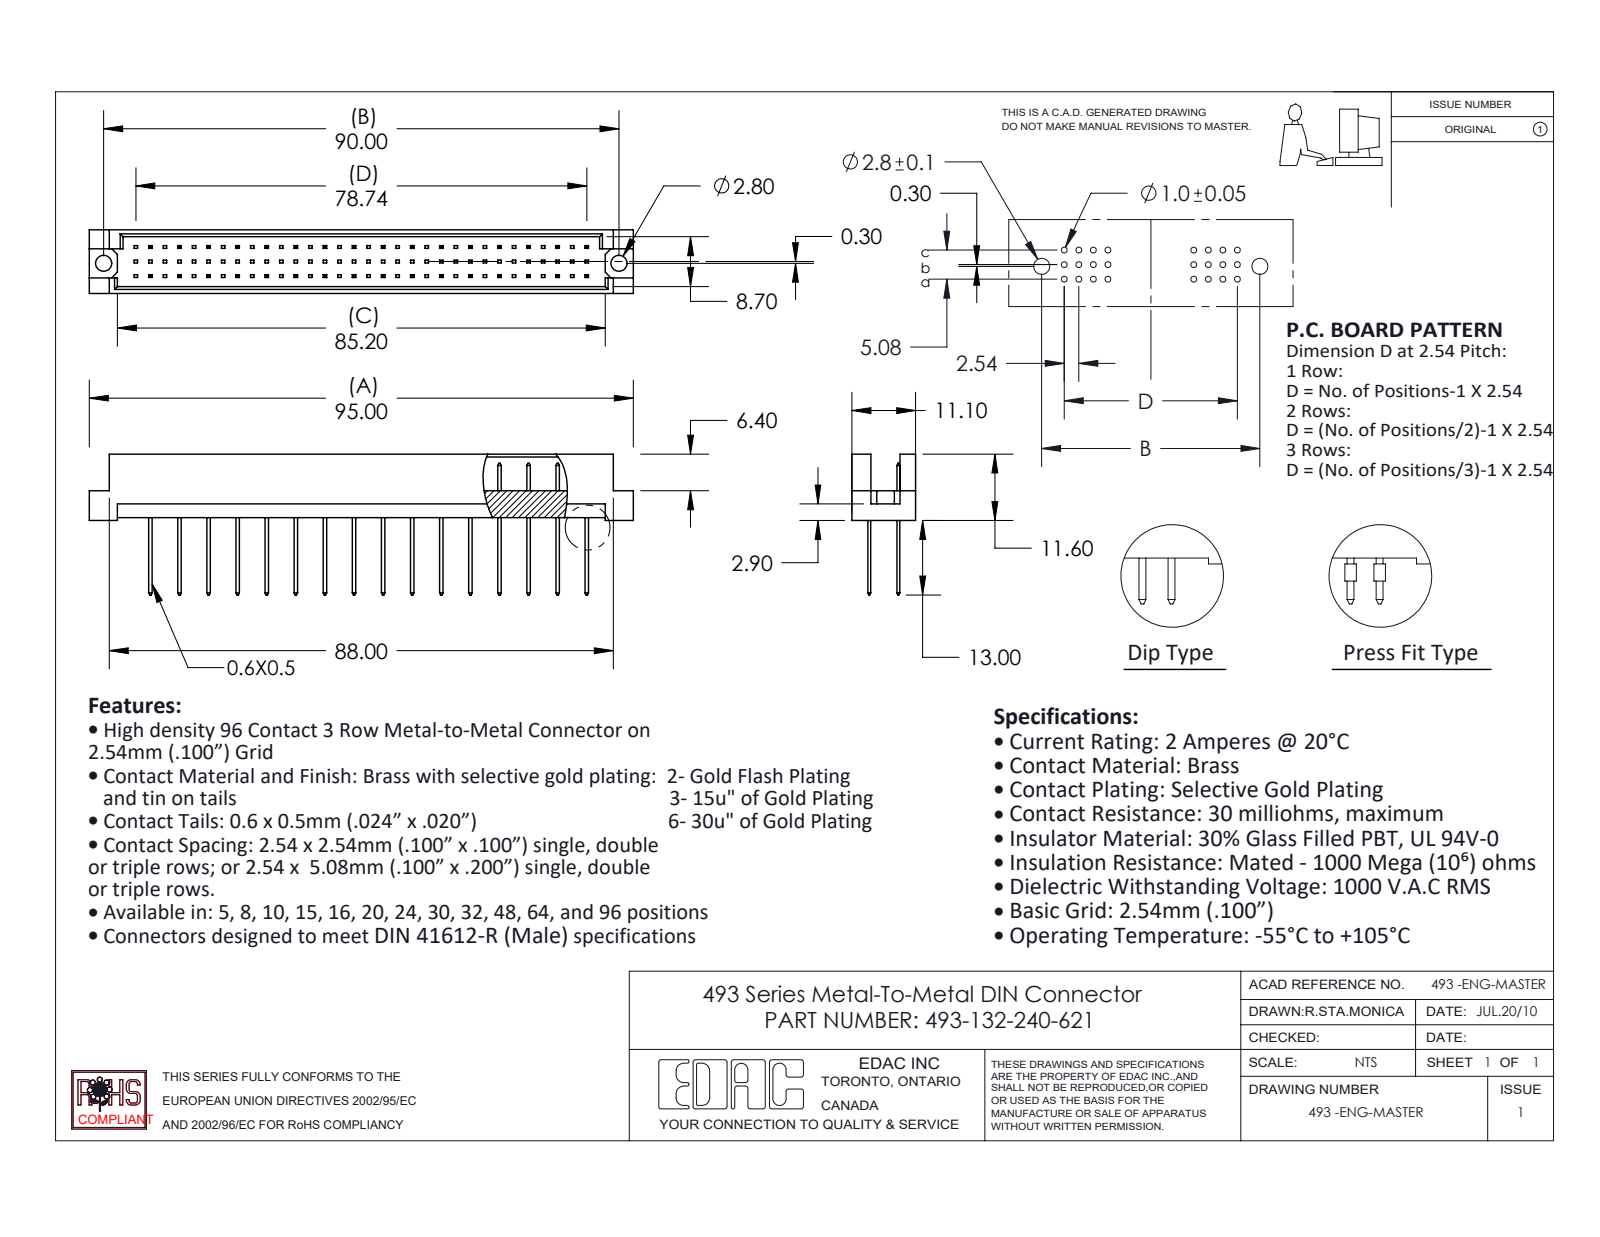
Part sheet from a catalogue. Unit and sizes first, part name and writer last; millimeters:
Units: millimetres
Overall size (bounding box): 95 × 24.6 × 11.1
Round holes (diameter × count): ⌀2.8 ×2
Main face-to-face distances: 1.2, 9.9, 5.08, 11.1, 8.7, 0.5, 4.7, 2.76, 3.26, 7.84
Hole centre spacings: 90
Volume: 5 876 mm³ · Surface area: 8 081 mm²
Bodies: 33 solids, 884 faces (880 planar, 4 cylindrical, 0 other)
Part name (STEP PRODUCT): 493 Part_96; 493-132-240-621; 493-290_40
STEP written by: SolidWorks 2020 (CONFIG_CONTROL_DESIGN)
